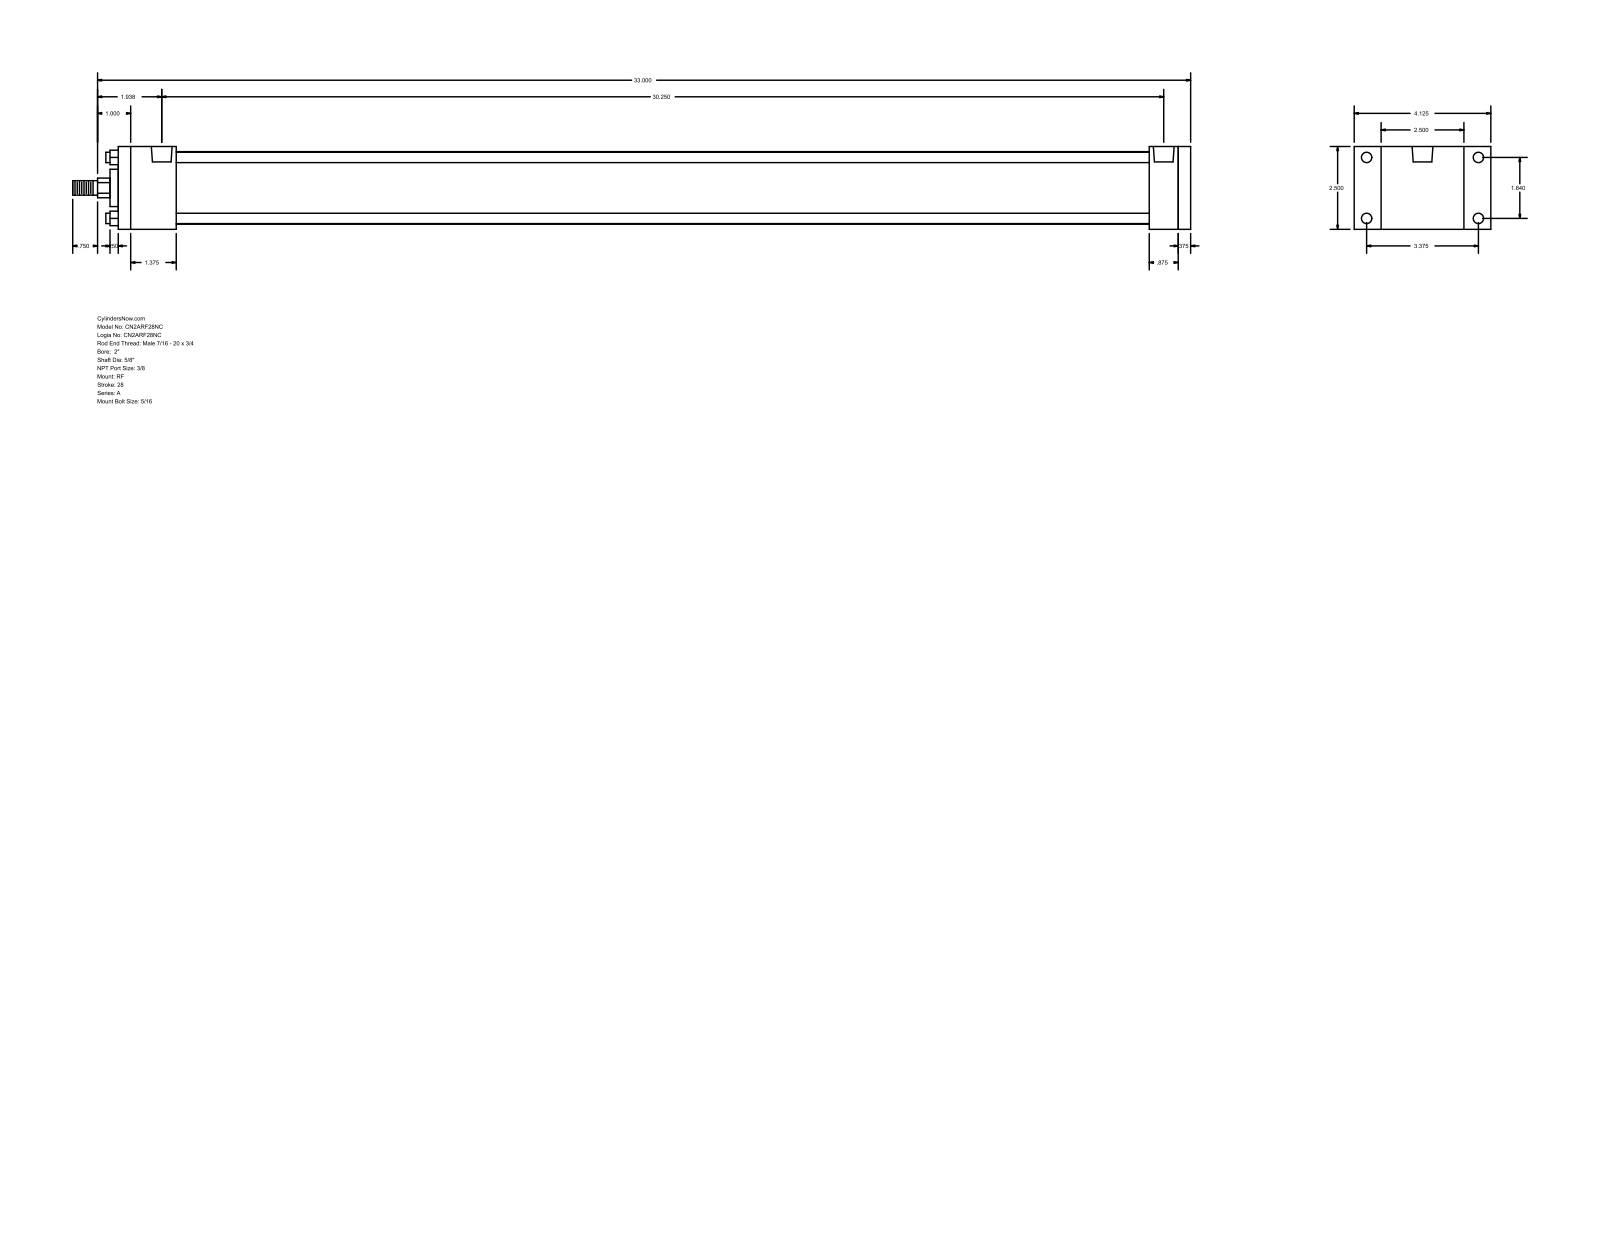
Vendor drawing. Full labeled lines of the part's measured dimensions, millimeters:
Part name (STEP PRODUCT): A_RF__0200_0.625
STEP written by: GSSL Pune (CONFIG_CONTROL_DESIGN)
Units: millimetres
Bodies: 0 solids, 92 faces (64 planar, 28 cylindrical, 0 other)
Overall size (bounding box): 857.25 × 104.78 × 63.5
Round holes (diameter × count): ⌀5.56 ×4, ⌀7.94 ×4, ⌀15.93 ×2
Round bosses / shafts (diameter × count): ⌀7.94 ×4, ⌀55.63 ×1, ⌀28.57 ×1, ⌀15.88 ×1, ⌀11.11 ×1
Partial cylindrical surfaces — rounded edges, fillets, slot ends (radius × count): R7.54 ×1
Main face-to-face distances: 63.5, 822.32, 9.53, 812.79, 44.45, 768.34, 777.87, 790.57, 746.12, 22.22
Hole centre spacings: 46.74, 85.72, 97.63, 760.4, 3.97, 3.98, 764.37, 764.38
